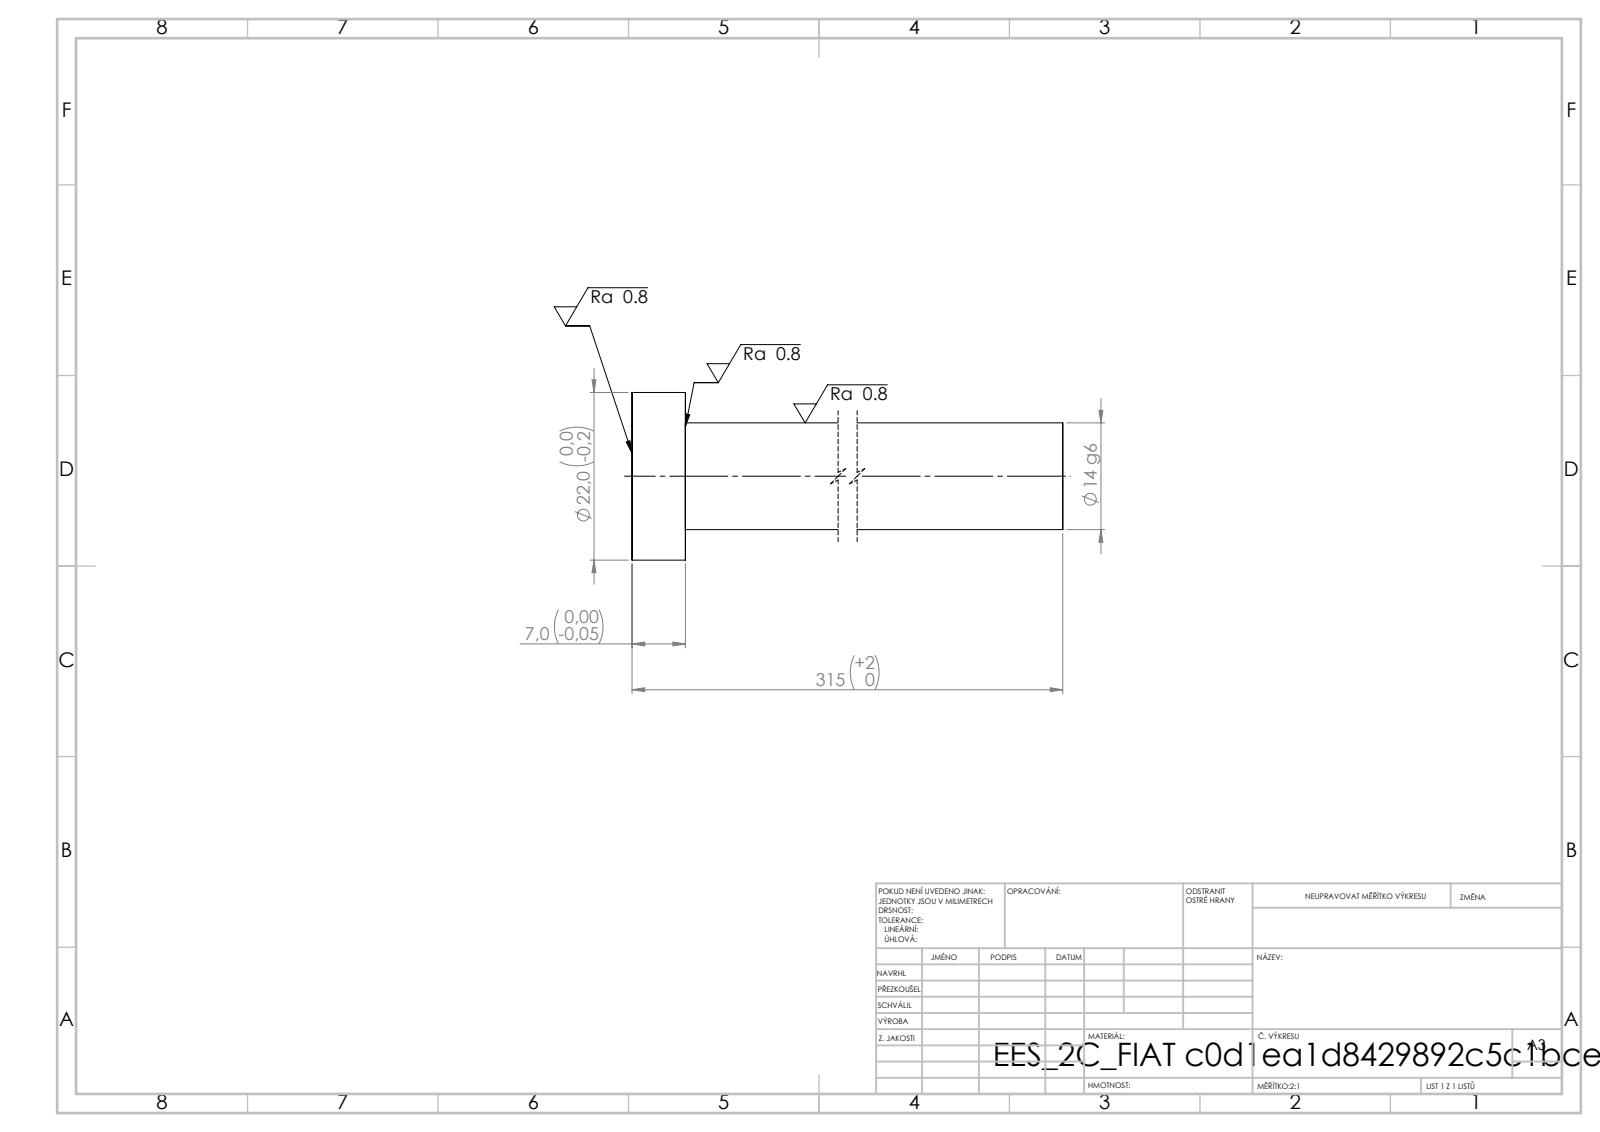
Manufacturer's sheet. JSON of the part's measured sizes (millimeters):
{"step_written_by": "SolidWorks 2019 (CONFIG_CONTROL_DESIGN)", "units": "millimeters", "bodies": {"solids": 1, "faces": 7, "planar": 3, "cylindrical": 4, "other": 0}, "overall_size": [315, 22, 22], "volume_mm3": 50074, "surface_area_mm2": 14791, "round_bosses_or_shafts": [[22, 1], [14, 1]], "face_to_face_distances": [7, 315, 308]}
